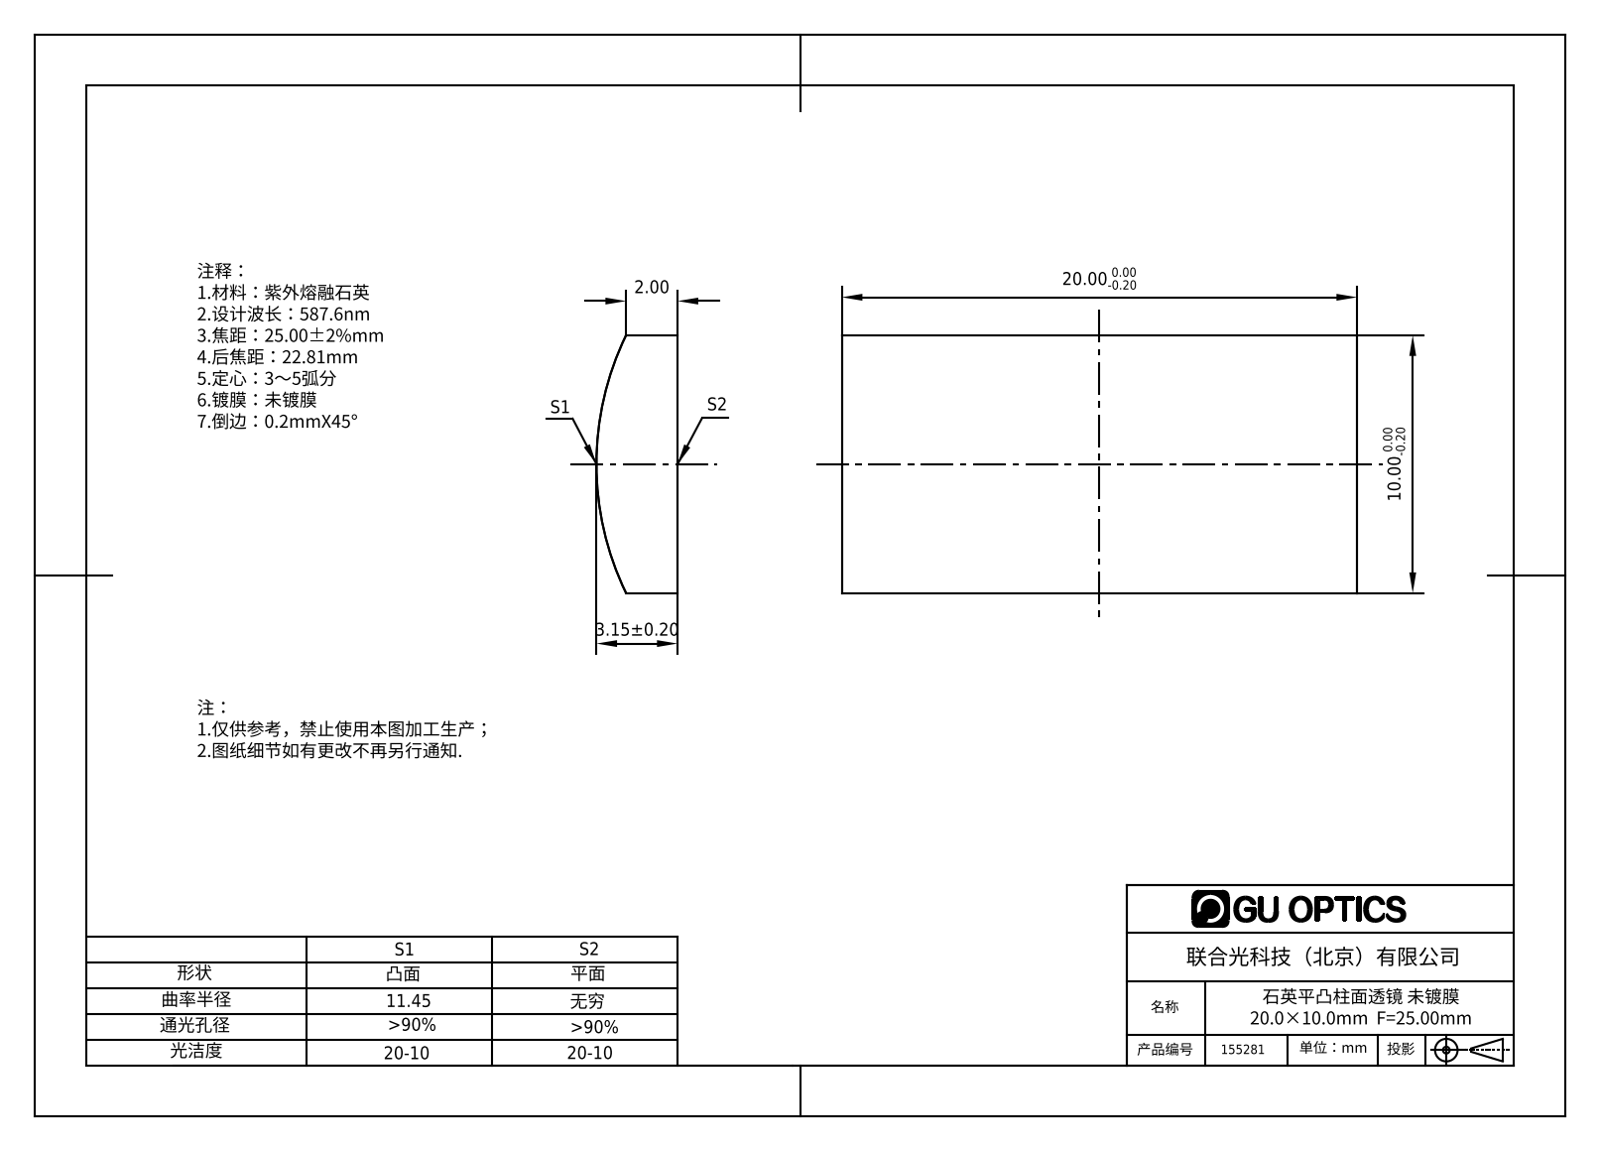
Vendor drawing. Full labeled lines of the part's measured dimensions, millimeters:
Part name (STEP PRODUCT): 155281
STEP written by: SolidWorks 2016 (AUTOMOTIVE_DESIGN)
Units: millimetres
Bodies: 1 solid, 6 faces (5 planar, 1 cylindrical, 0 other)
Overall size (bounding box): 20 × 10 × 3.15
Volume: 555 mm³ · Surface area: 542 mm²
Partial cylindrical surfaces — rounded edges, fillets, slot ends (radius × count): R11.45 ×1
Main face-to-face distances: 10, 20
